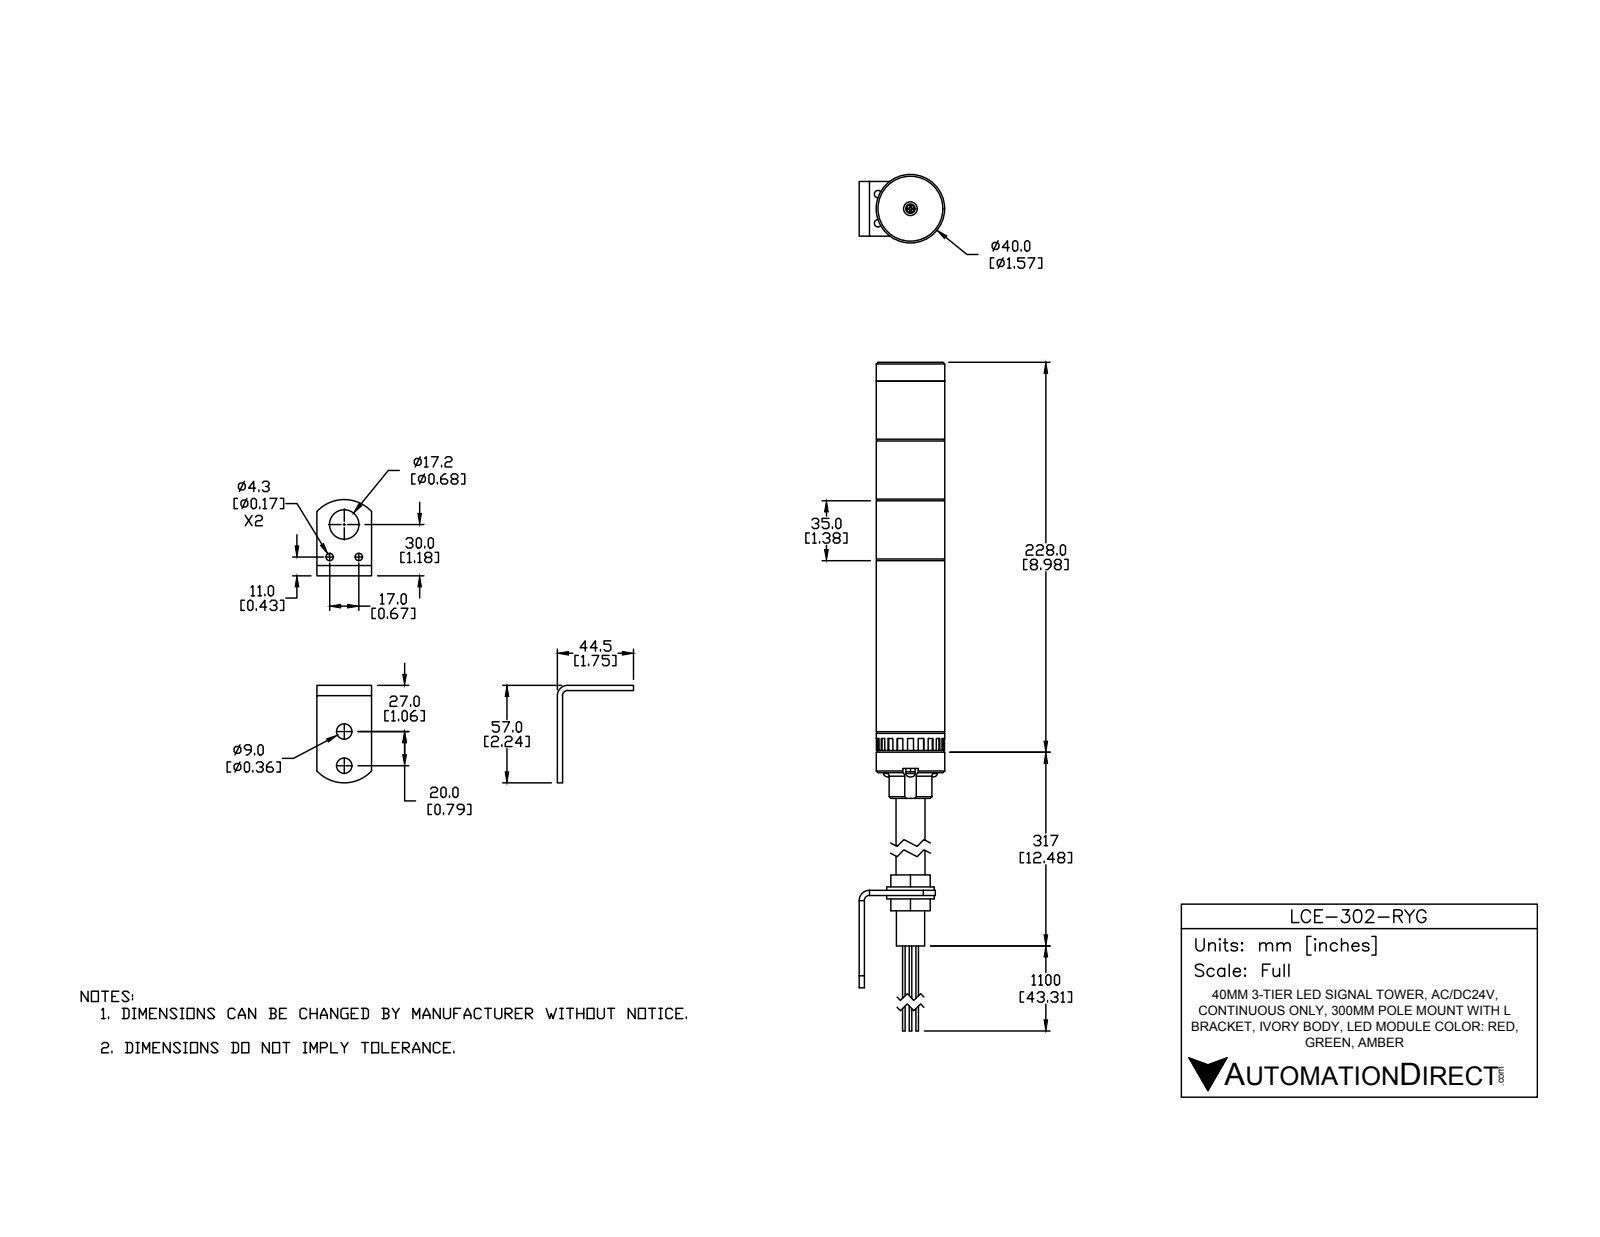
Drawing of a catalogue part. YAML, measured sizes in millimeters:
part_name: "LCE-302-RYG"
step_written_by: "SolidWorks 2016 (AUTOMOTIVE_DESIGN)"
units: millimeters
bodies: {solids: 31, faces: 369, planar: 237, cylindrical: 112, other: 20}
overall_size: [628, 50, 40]
volume: 351505
surface_area: 114631
round_holes:
  - {diameter: 3.5, count: 3}
  - {diameter: 4, count: 3}
  - {diameter: 4.3, count: 2}
  - {diameter: 9.04, count: 2}
  - {diameter: 8, count: 1}
  - {diameter: 12, count: 1}
  - {diameter: 17.2, count: 1}
  - {diameter: 17.5, count: 1}
  - {diameter: 18, count: 1}
round_bosses_or_shafts:
  - {diameter: 1.5, count: 6}
  - {diameter: 5.5, count: 4}
  - {diameter: 3, count: 3}
  - {diameter: 40, count: 1}
  - {diameter: 39.5, count: 1}
  - {diameter: 38.5, count: 1}
  - {diameter: 27.8, count: 1}
  - {diameter: 17, count: 1}
partial_cylinders:
  - {radius: 4.5, count: 3}
  - {radius: 21.79, count: 2}
  - {radius: 3, count: 1}
  - {radius: 6, count: 1}
  - {radius: 12.5, count: 1}
face_to_face_distances: [35, 1, 70, 34, 11, 36, 69, 101, 136, 171]
hole_center_spacings: [15, 25.98, 20.81, 6.09, 17, 17.09, 20, 20.08]
